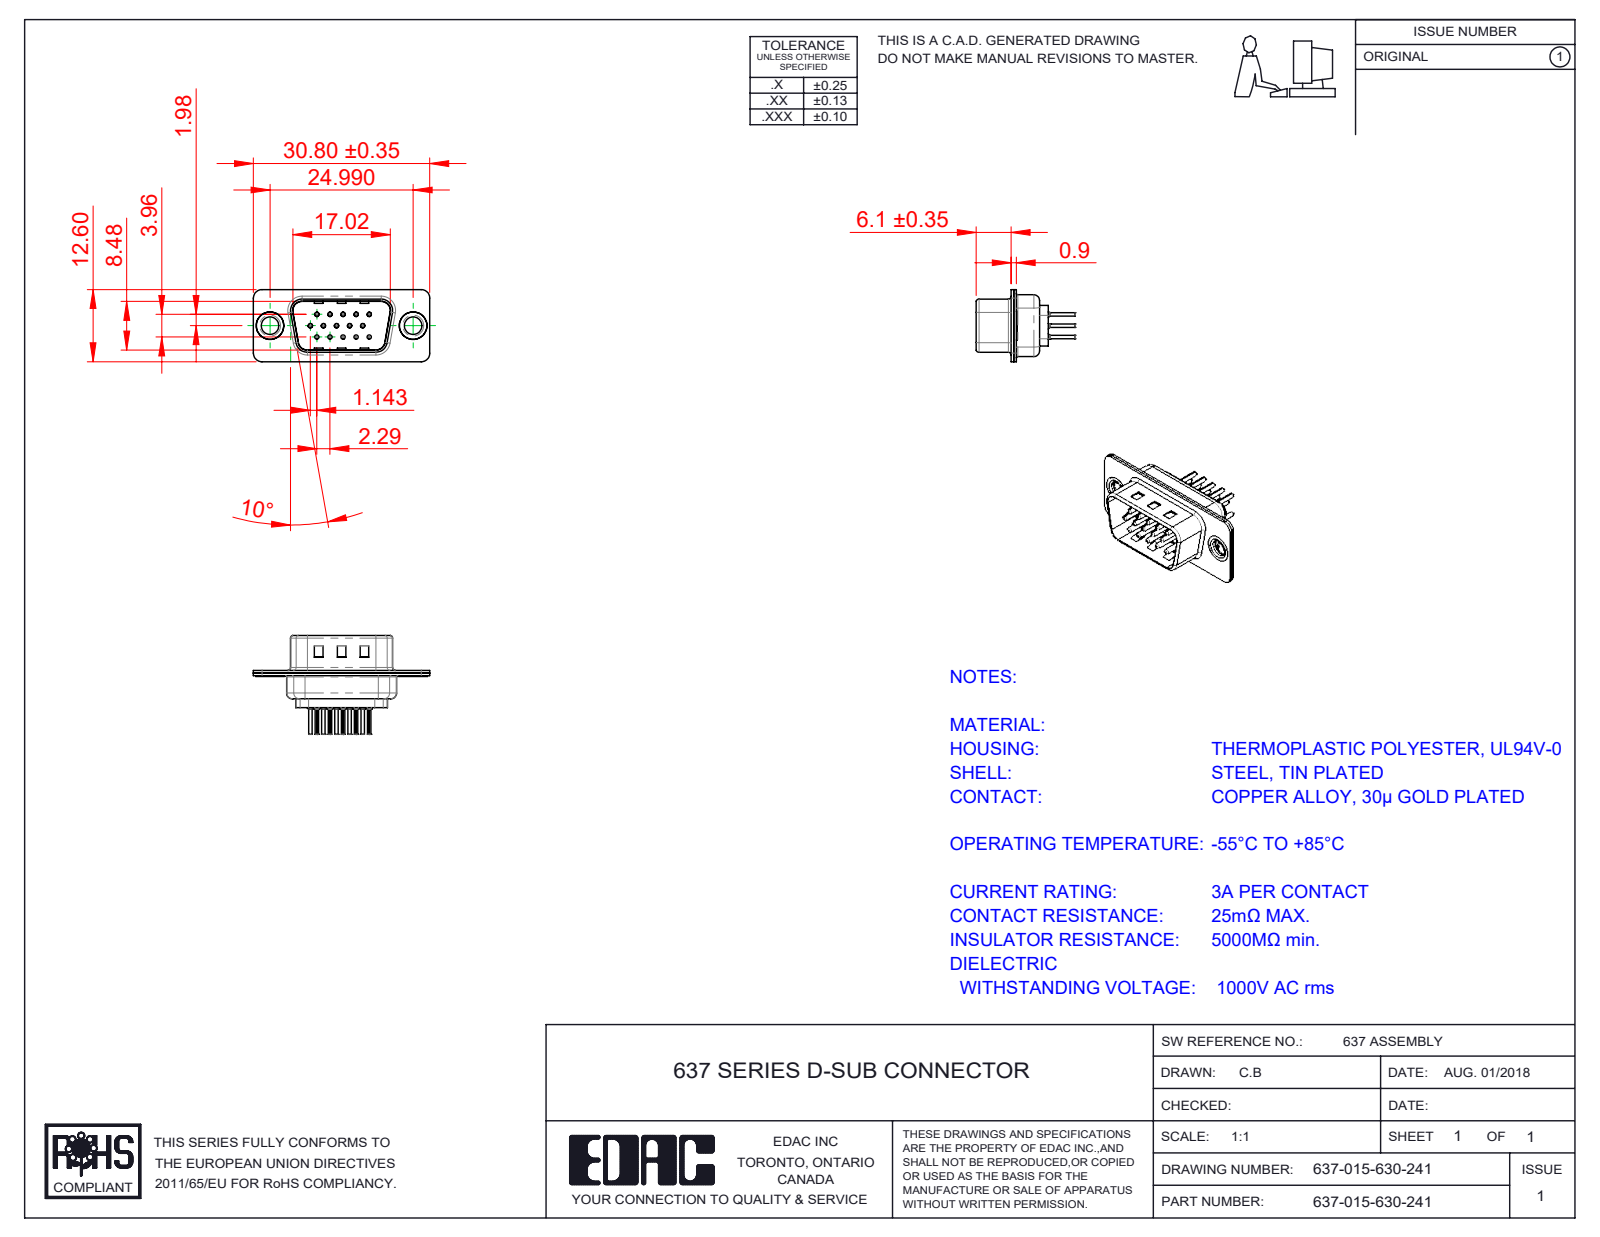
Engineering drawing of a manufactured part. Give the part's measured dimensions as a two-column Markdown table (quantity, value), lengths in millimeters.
| quantity | value |
| --- | --- |
| part name | 637 Shell Front_15 Contacts; 637 Contact Row 1_30; 637 Contact Row 3_30; 637 Shell Rear_15 Contacts (+4 more) |
| STEP written by | SolidWorks 2020 (CONFIG_CONTROL_DESIGN) |
| units | millimeters |
| bodies | 20 solids, 1778 faces (467 planar, 668 cylindrical, 643 other) |
| overall size | 30.8 × 17.25 × 12.6 |
| volume | 1 238 mm³ |
| surface area | 4 501 mm² |
| round holes (diameter × count) | 0.2 × 15, 0.35 × 15, 1.1 × 15, 1.6 × 15, 3.05 × 2, 4 × 2, 4.8 × 2 |
| round bosses / shafts (diameter × count) | 2 × 15, 1.5 × 15, 0.75 × 15, 0.6 × 15, 5 × 2, 4.9 × 2, 3.55 × 2 |
| partial cylindrical surfaces (radius × count) | 0.1 × 30, 1.5 × 16, 2 × 12, 0.5 × 8, 0.25 × 4, 0.55 × 4, 0.7 × 4, 0.95 × 4 |
| main face-to-face distances | 0.45, 0.9, 0.4, 1.05, 0.7, 8.88, 8.48, 0.31, 4.55, 1.16 |
| hole center spacings | 3.96, 2.28, 4.57, 2.29, 6.05, 6.86, 7.92, 6.04 |
